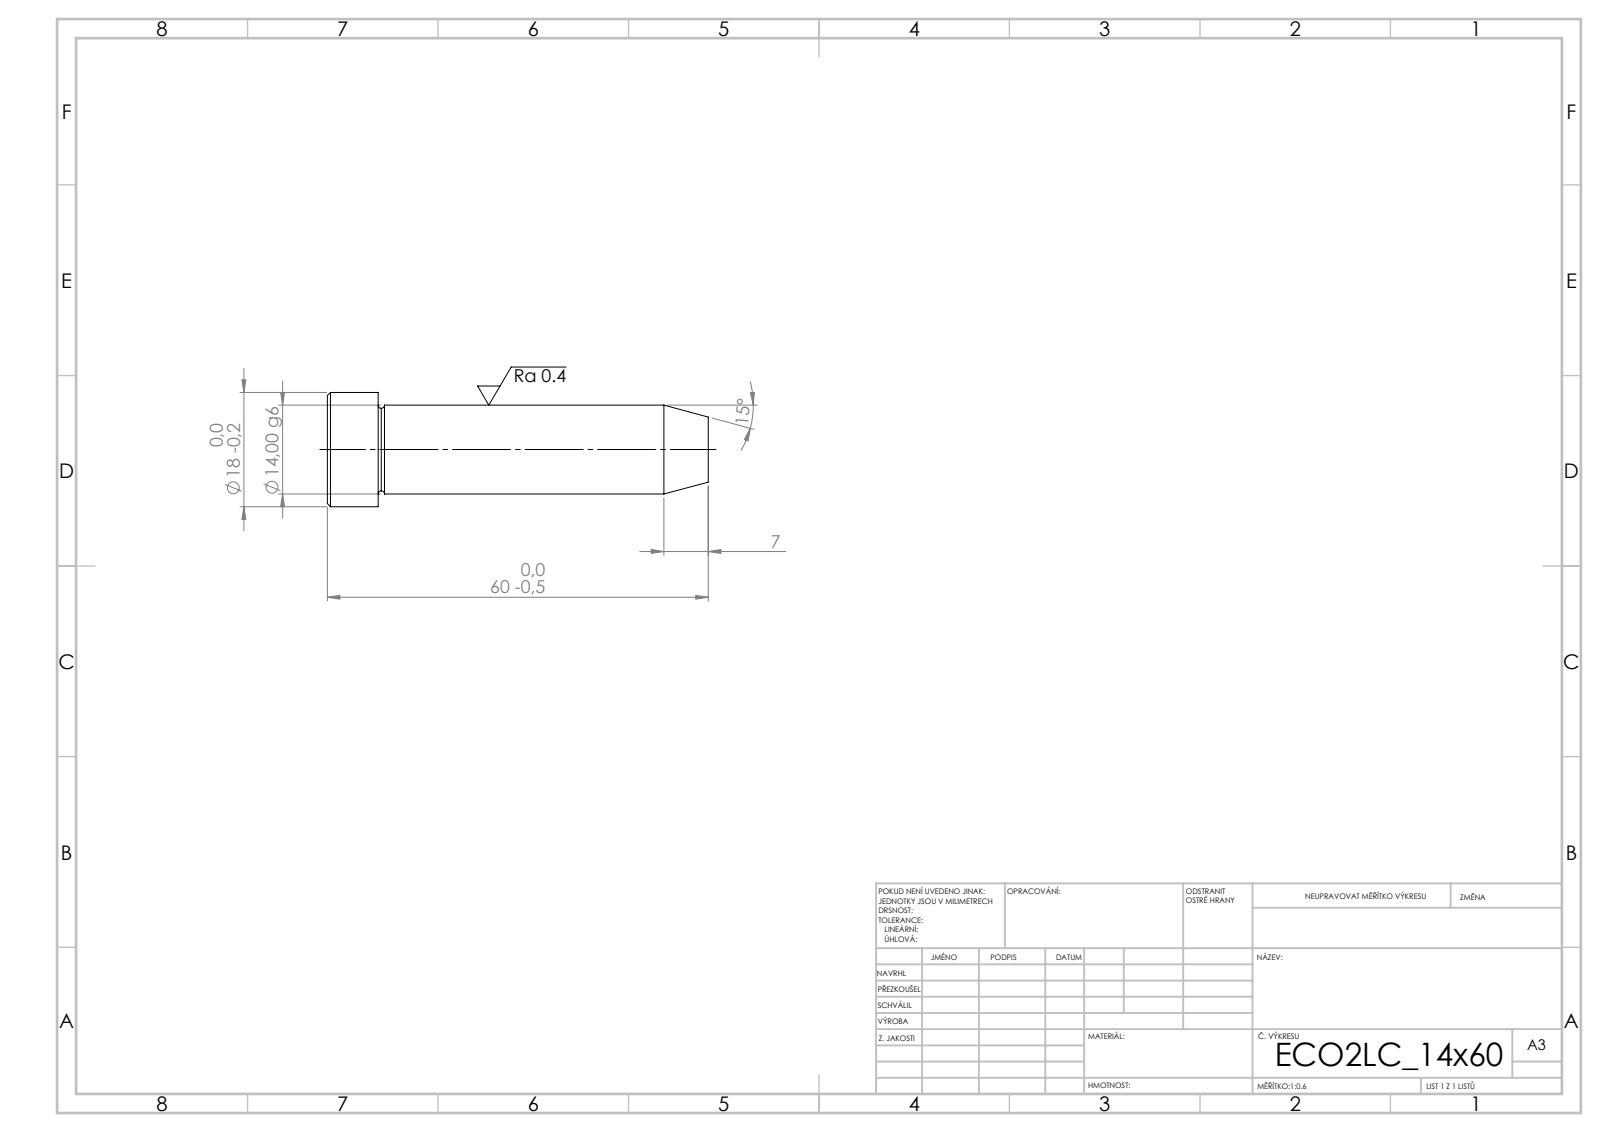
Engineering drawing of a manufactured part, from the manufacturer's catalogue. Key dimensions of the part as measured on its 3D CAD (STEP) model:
STEP written by: SolidWorks 2019 (CONFIG_CONTROL_DESIGN)
Units: millimetres
Bodies: 1 solid, 15 faces (3 planar, 4 cylindrical, 8 other)
Overall size (bounding box): 60 × 18 × 18
Volume: 9 754 mm³ · Surface area: 3 150 mm²
Round bosses / shafts (diameter × count): ⌀18 ×1, ⌀14 ×1
Main face-to-face distances: 8, 52, 60
